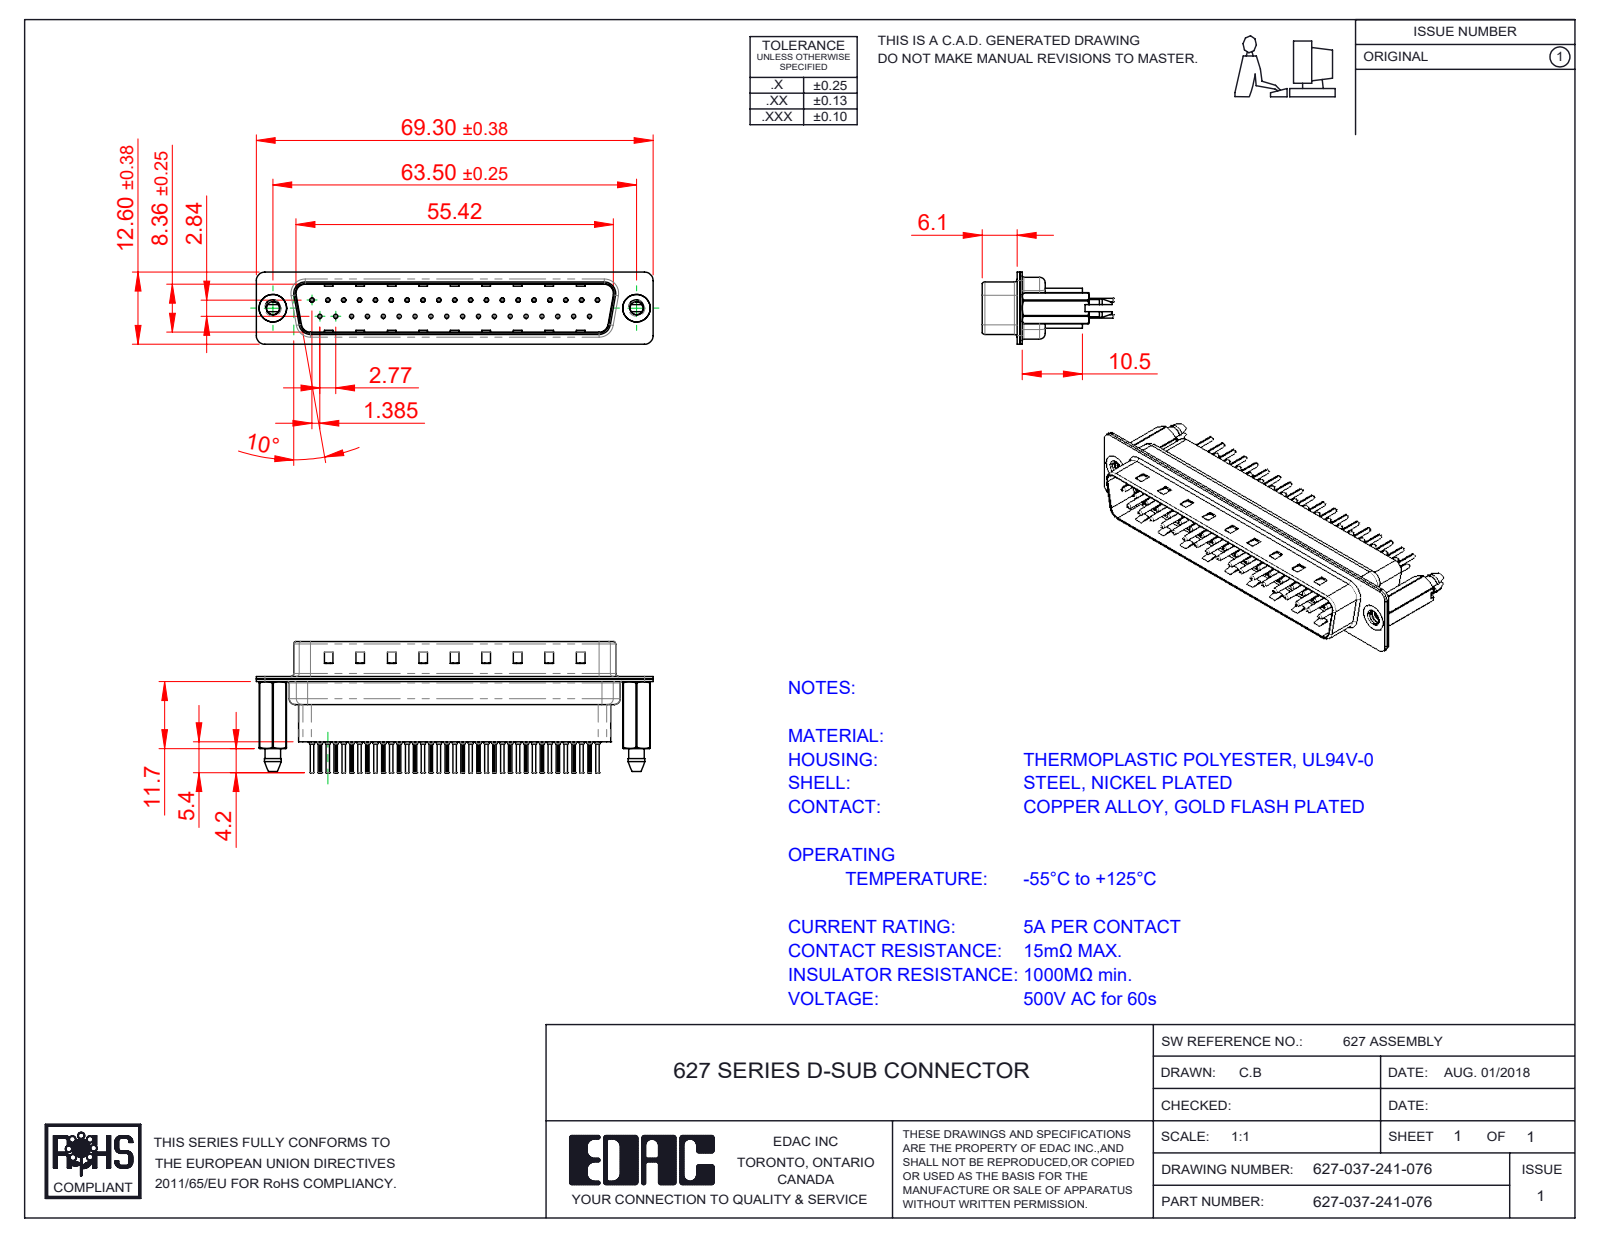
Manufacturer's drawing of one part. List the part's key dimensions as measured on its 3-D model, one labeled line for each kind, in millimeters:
Part name (STEP PRODUCT): 627 Shell Front_37 Contacts; 627 Shell Rear_37 Contacts; 627 Contact Row 1_41; 627 4-40 Threaded Boardlock_HP41 (+3 more)
STEP written by: SolidWorks 2020 (CONFIG_CONTROL_DESIGN)
Units: millimetres
Bodies: 42 solids, 4146 faces (1123 planar, 1576 cylindrical, 1447 other)
Overall size (bounding box): 69.3 × 22.8 × 12.6
Volume: 5 605 mm³ · Surface area: 14 398 mm²
Round holes (diameter × count): ⌀0.2 ×37, ⌀0.35 ×37, ⌀1.1 ×37, ⌀1.6 ×37, ⌀2.26 ×2, ⌀4 ×2, ⌀4.8 ×2
Round bosses / shafts (diameter × count): ⌀2 ×37, ⌀1.5 ×37, ⌀0.75 ×37, ⌀0.6 ×37, ⌀4.9 ×2
Partial cylindrical surfaces — rounded edges, fillets, slot ends (radius × count): R0.1 ×74, R1.5 ×18, R2 ×12, R1.6 ×10, R0.5 ×8, R0.25 ×4, R0.6 ×4, R0.65 ×4
Main face-to-face distances: 0.4, 0.82, 9.58, 0.68, 7.68, 0.45, 1.5, 1.08, 8.08, 8.76
Hole centre spacings: 3.16, 2.77, 5.54, 8.31, 5.04, 10.1, 11.08, 12.78
